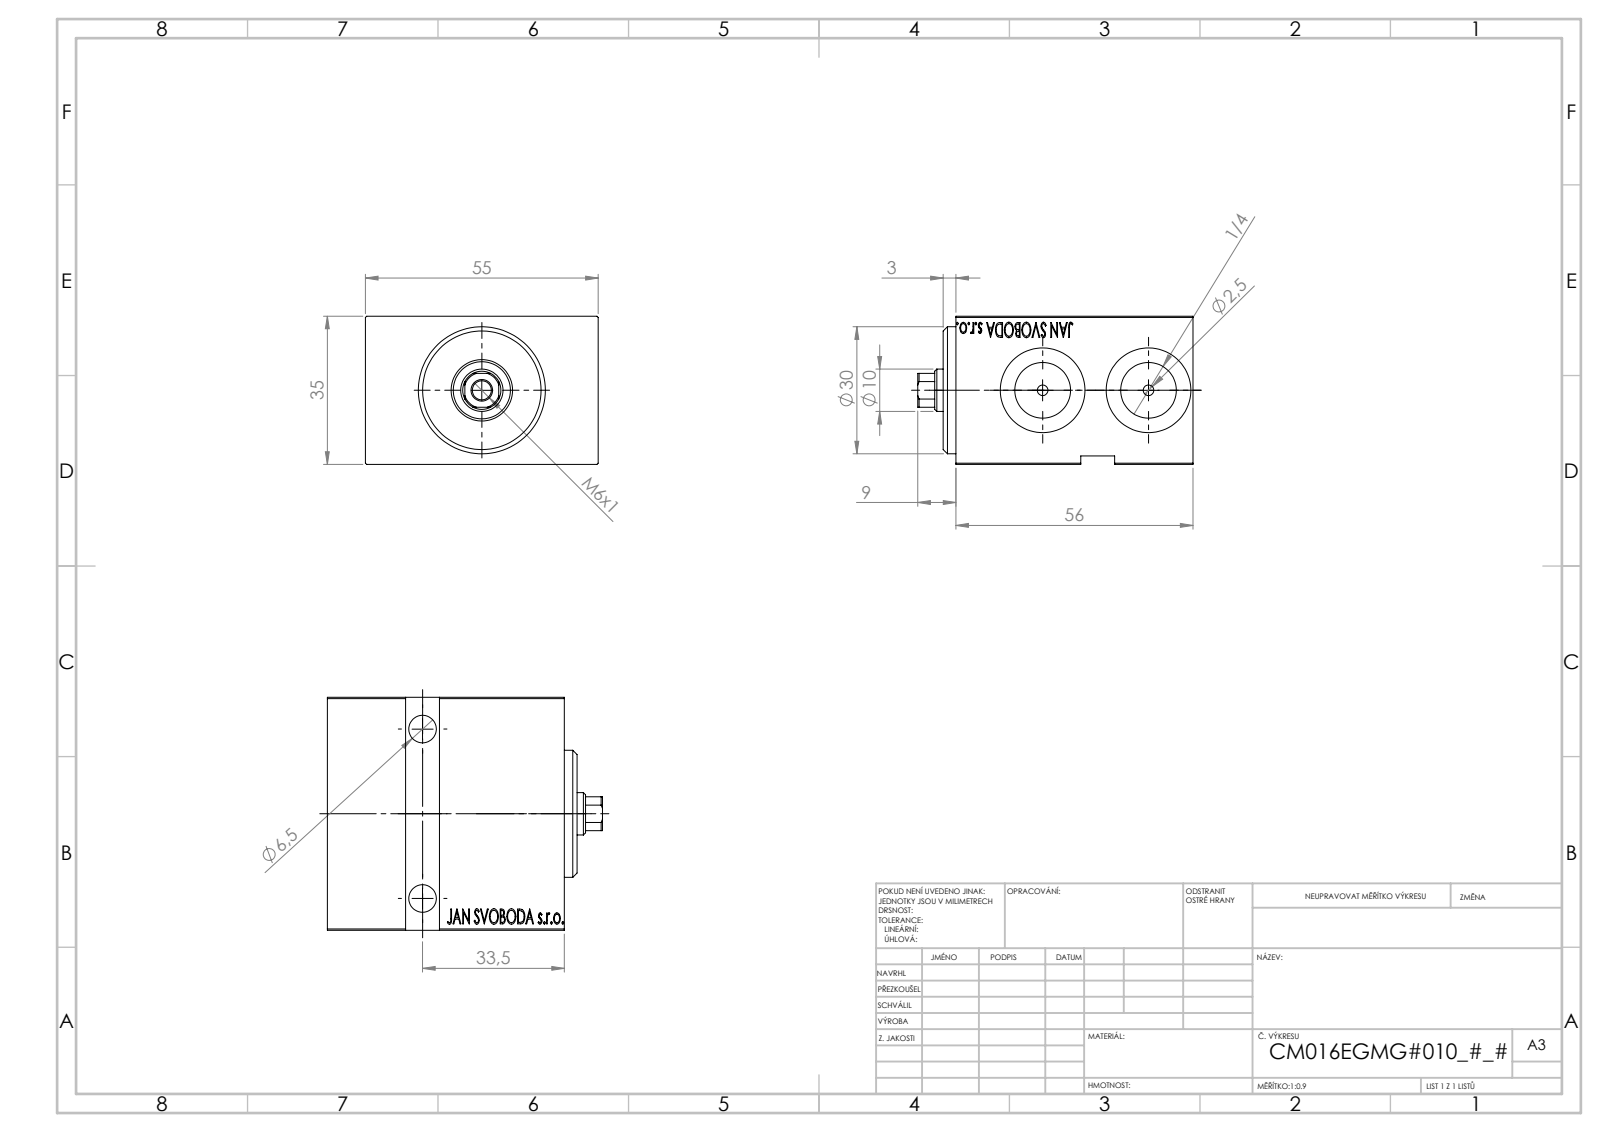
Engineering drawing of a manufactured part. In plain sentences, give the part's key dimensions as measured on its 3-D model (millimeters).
The part is named "V450CM_VC_B; V450CM_E_VCP; V450CM_E_Body". Its 3-D file was written by "SolidWorks 2019 (CONFIG_CONTROL_DESIGN)". It is 3 solids with 852 faces: 410 planar, 48 cylindrical and 394 other. Overall it measures 65 by 55 by 35 millimeters. Its volume is 100 029 cubic millimeters and its surface area 25 557 square millimeters. Round holes: 2 of diameter 2.5, 2 of diameter 6.5, 2 of diameter 10.5, 2 of diameter 13.16, 2 of diameter 20, 1 of diameter 4.5, 1 of diameter 10, 1 of diameter 13.5, 1 of diameter 14.5, 1 of diameter 16, 1 of diameter 18, 1 of diameter 25. Round bosses or shafts: 1 of diameter 30. Partial cylindrical surfaces (rounded edges, fillets, slot ends): 1 of radius 4.5. The main face-to-face distances are 35, 56, 55, 5, 51, 8, 3, 59, 46, 54. The hole center spacings are 25, 40.
